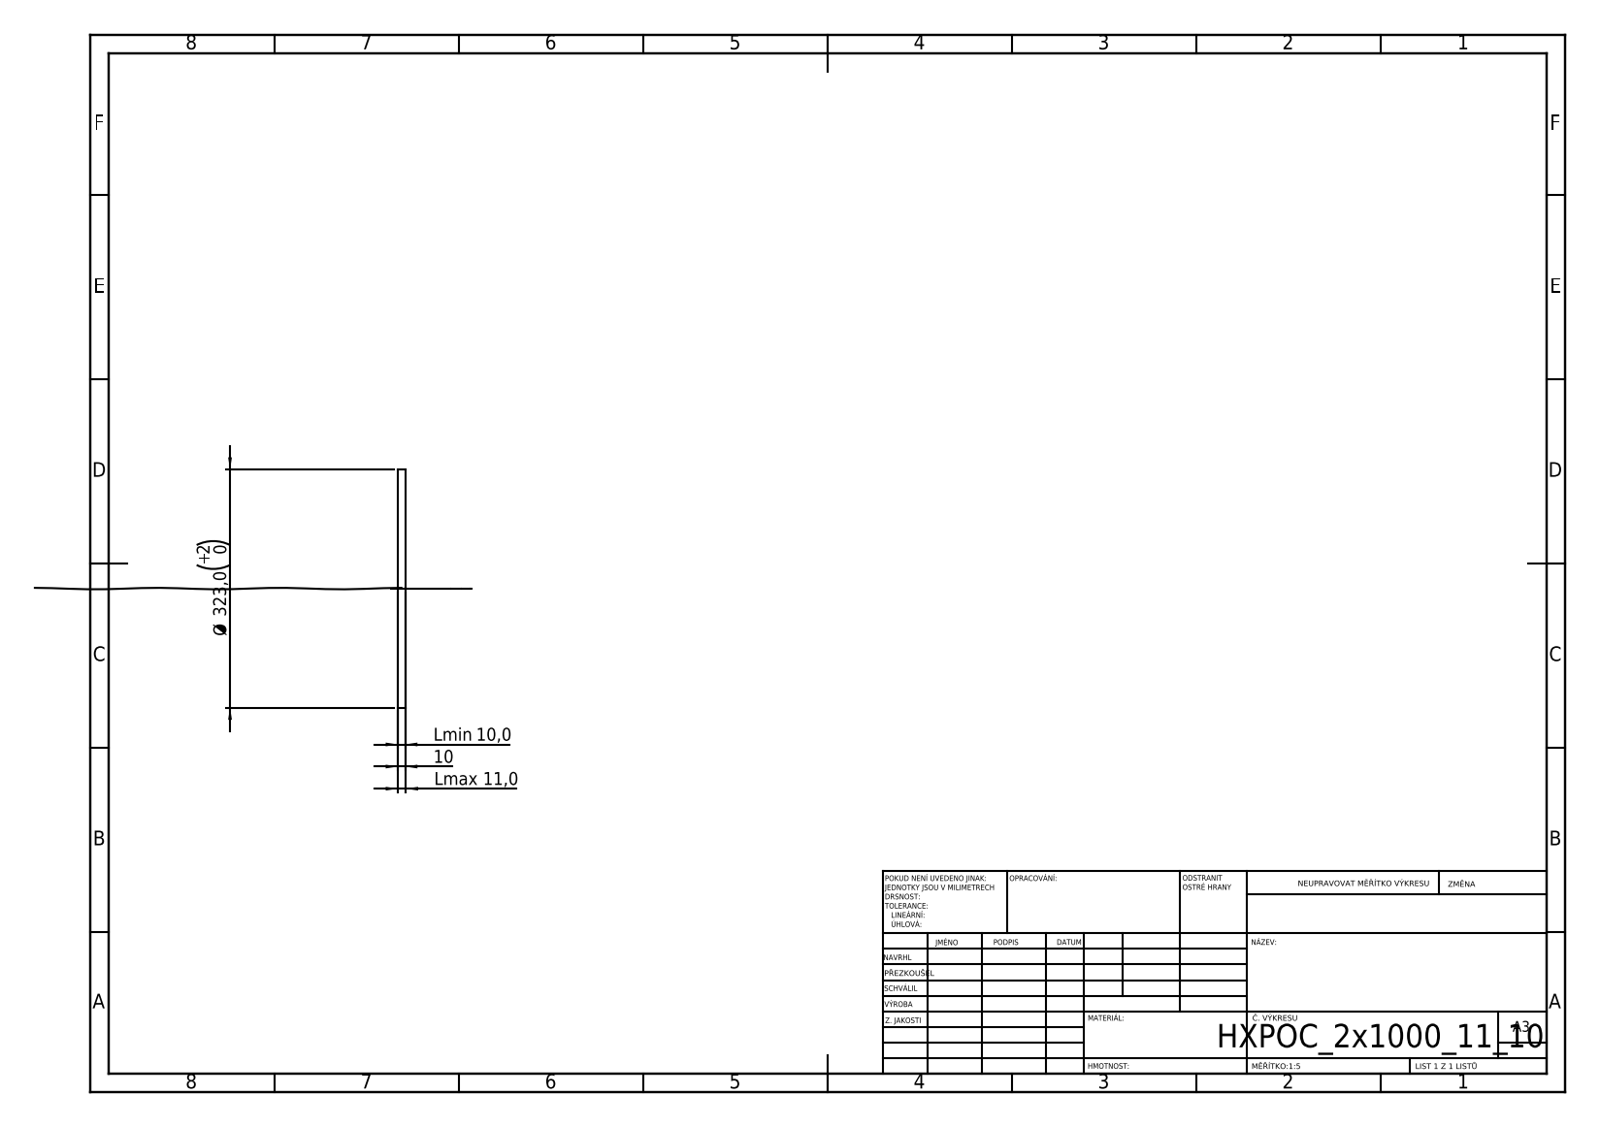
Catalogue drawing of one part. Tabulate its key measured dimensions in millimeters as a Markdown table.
| quantity | value |
| --- | --- |
| STEP written by | SolidWorks 2019 (CONFIG_CONTROL_DESIGN) |
| units | millimeters |
| bodies | 1 solid, 17 faces (7 planar, 8 cylindrical, 2 other) |
| overall size | 323 × 323 × 11 |
| volume | 819 400 mm³ |
| surface area | 174 046 mm² |
| round holes (diameter × count) | 2 × 1 |
| round bosses / shafts (diameter × count) | 323 × 1, 1.6 × 1 |
| main face-to-face distances | 10, 11, 1, 6.67, 3.33, 4.33, 6.27, 0.4, 3.73, 4.73 |
